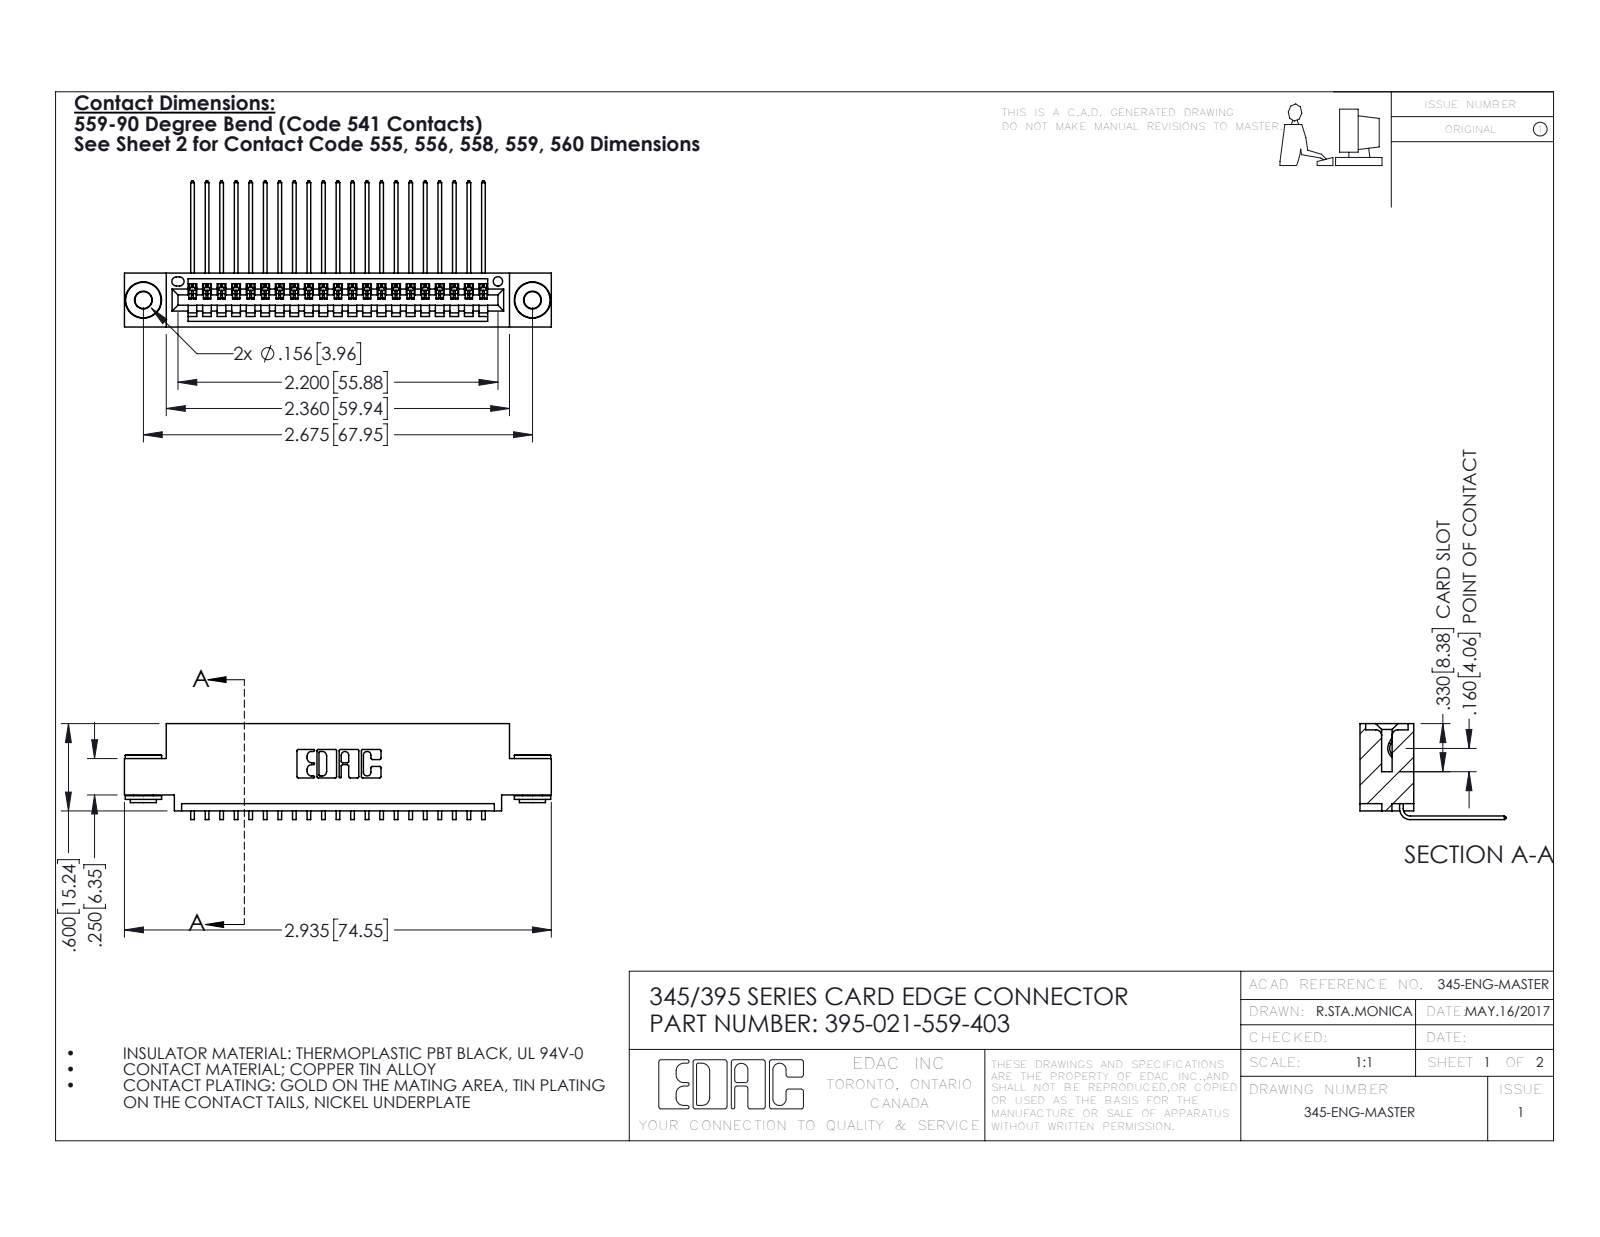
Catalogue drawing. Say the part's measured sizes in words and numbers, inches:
The part is named "345-250-002_345-250-002-102; 345-292-001_558 559 Tail - 1; 345 Part_0.110 Offset - 0.156 Dia-TH; 395-021-559-403". Its 3-D file was written by "SolidWorks 2016 (CONFIG_CONTROL_DESIGN)". It is 24 solids with 1428 faces: 976 planar, 444 cylindrical and 8 other. Overall it measures 2.935 by 1.005 by 0.659 inches. Its volume is 0.423 cubic inches and its surface area 14.92 square inches. Round holes: 2 of diameter 0.116, 2 of diameter 0.156, 1 of diameter 0.064. Round bosses or shafts: 2 of diameter 0.25, 2 of diameter 0.18, 2 of diameter 0.136. Partial cylindrical surfaces (rounded edges, fillets, slot ends): 42 of radius 0.006, 22 of radius 0.01, 6 of radius 0.007, 6 of radius 0.031, 3 of radius 0.026, 2 of radius 0.031, 2 of radius 0.04, 1 of radius 0.014. The main face-to-face distances are 0.072, 0.298, 0.37, 0.2, 0.025, 0.098, 0.272, 0.225, 0.149, 0.072. The hole center spacings are 0.27, 2.441, 2.675.
